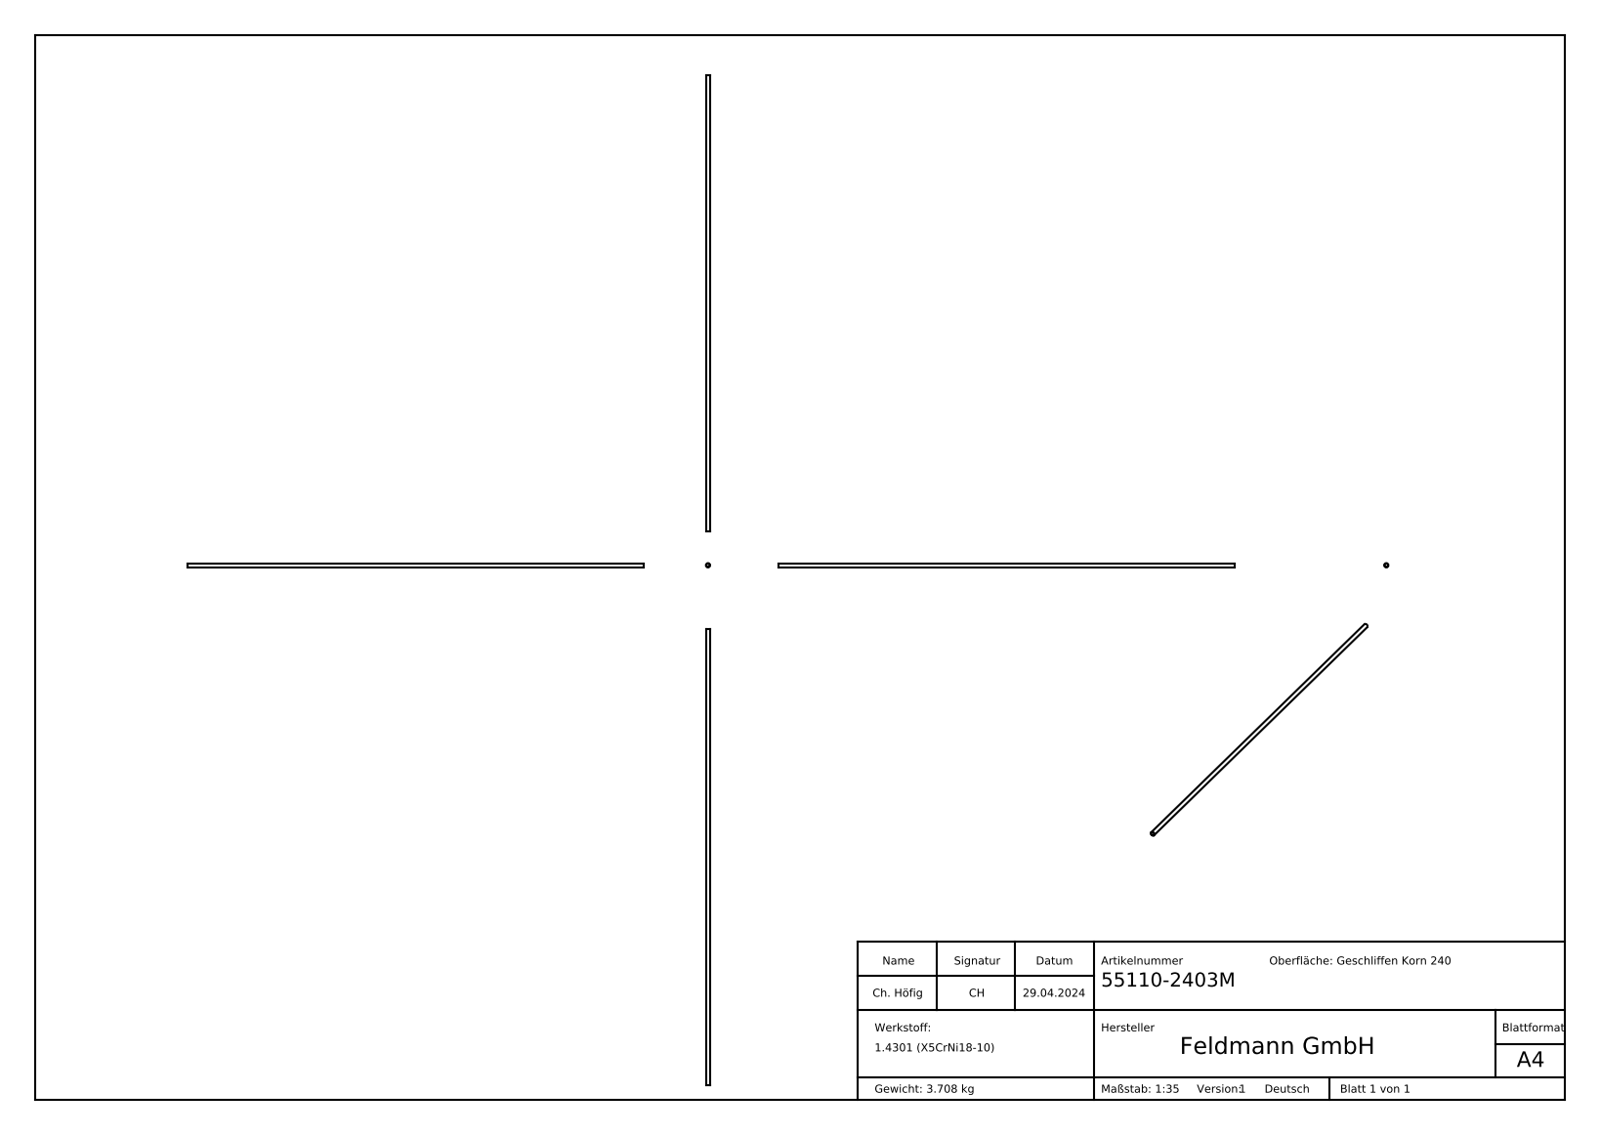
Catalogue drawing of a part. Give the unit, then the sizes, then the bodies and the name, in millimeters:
Units: millimetres
Overall size (bounding box): 3000 × 26.9 × 26.9
Round holes (diameter × count): ⌀22.9 ×1
Round bosses / shafts (diameter × count): ⌀26.9 ×1
Partial cylindrical surfaces — rounded edges, fillets, slot ends (radius × count): R11.55 ×1
Main face-to-face distances: 3000, 0.73, 0.61, 0.63, 1.57, 0.76, 1.24, 0.79, 0.93, 0.65
Volume: 469 354 mm³ · Surface area: 469 675 mm²
Bodies: 1 solid, 291 faces (141 planar, 28 cylindrical, 122 other)
Part name (STEP PRODUCT): 55110-2403M
STEP written by: SolidWorks 2018 (CONFIG_CONTROL_DESIGN)
